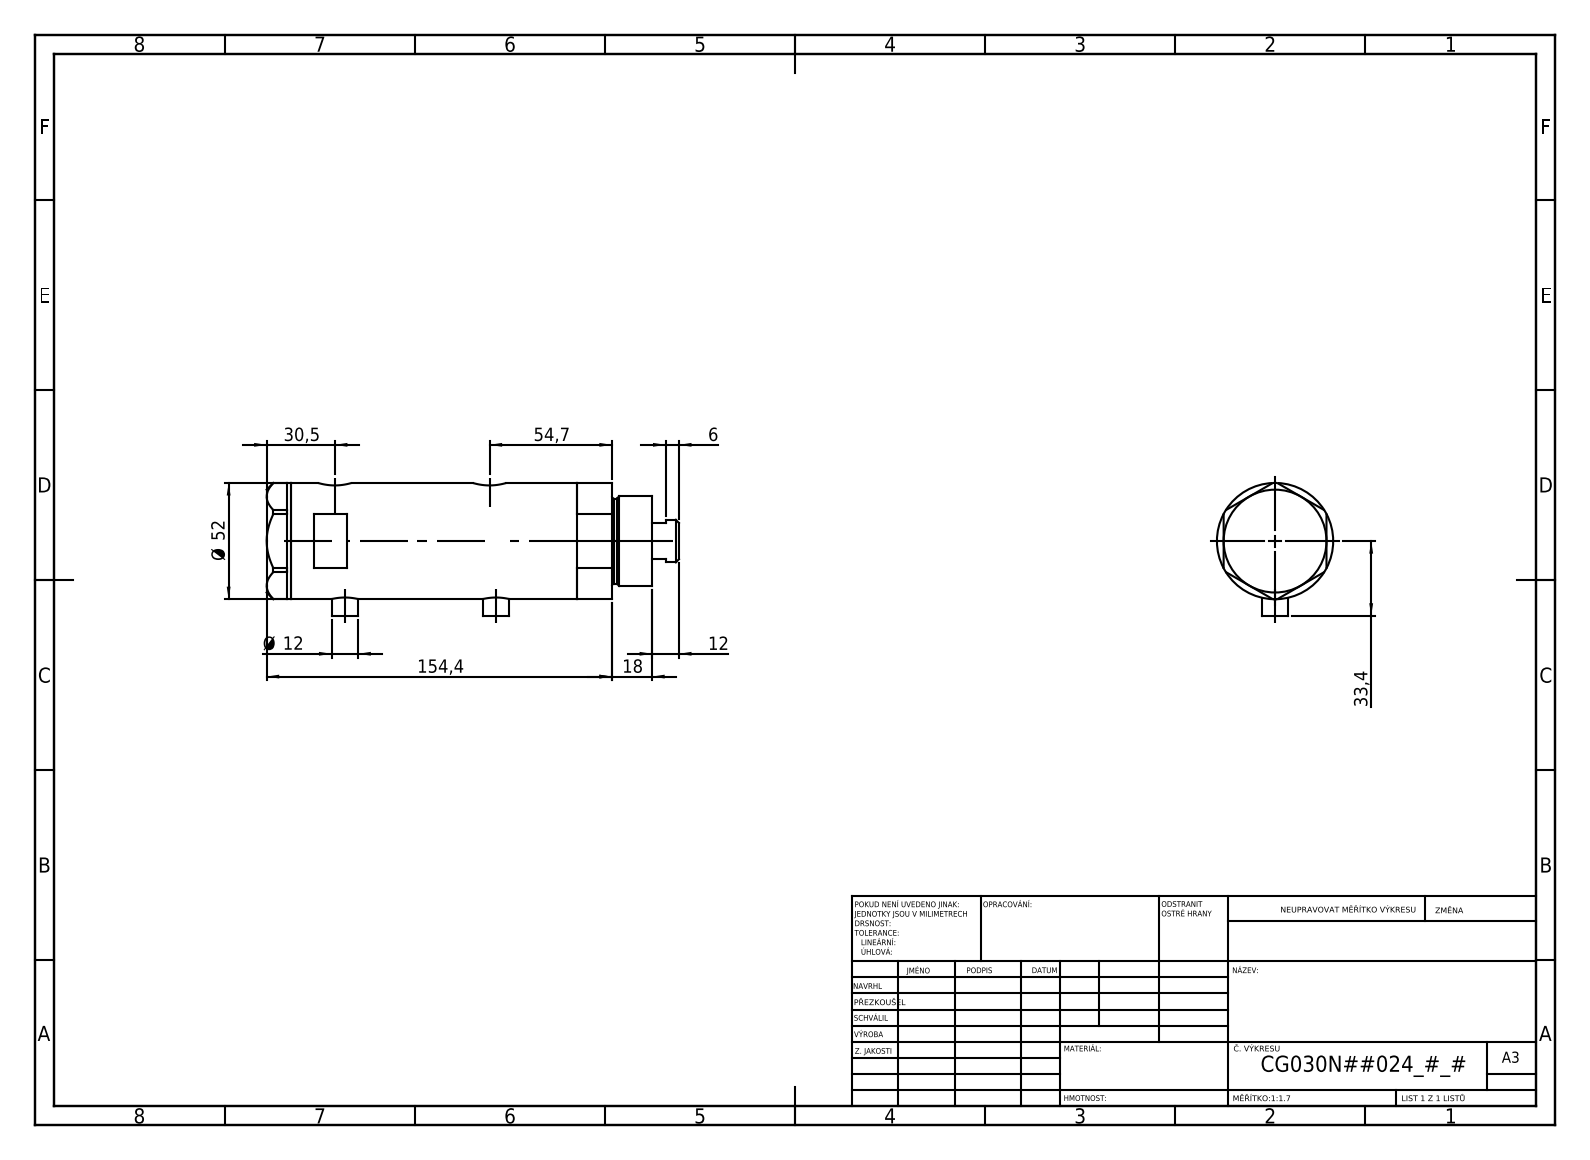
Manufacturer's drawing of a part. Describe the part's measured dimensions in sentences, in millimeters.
The part is named "V270CG_FRONT; V270CG_VC; V270CG_BACK; V270CG_MIDDLE". Its 3-D file was written by "SolidWorks 2019 (CONFIG_CONTROL_DESIGN)". It is 4 solids with 134 faces: 65 planar, 49 cylindrical and 20 other. Overall it measures 184.4 by 59.4 by 52 millimeters. Its volume is 337 276 cubic millimeters and its surface area 77 323 square millimeters. Round holes: 2 of diameter 9.73, 2 of diameter 12.5, 2 of diameter 15, 1 of diameter 6.5, 1 of diameter 20, 1 of diameter 21.5, 1 of diameter 30, 1 of diameter 33, 1 of diameter 44. Round bosses or shafts: 2 of diameter 12, 1 of diameter 52, 1 of diameter 40, 1 of diameter 38, 1 of diameter 19. The main face-to-face distances are 91.5, 23.8, 67.7, 11, 34.8, 102.5, 46, 138.9, 127.9, 104.1. The hole center spacings are 2.9, 4.5, 64.7, 67.6, 69.2, 72.1.
